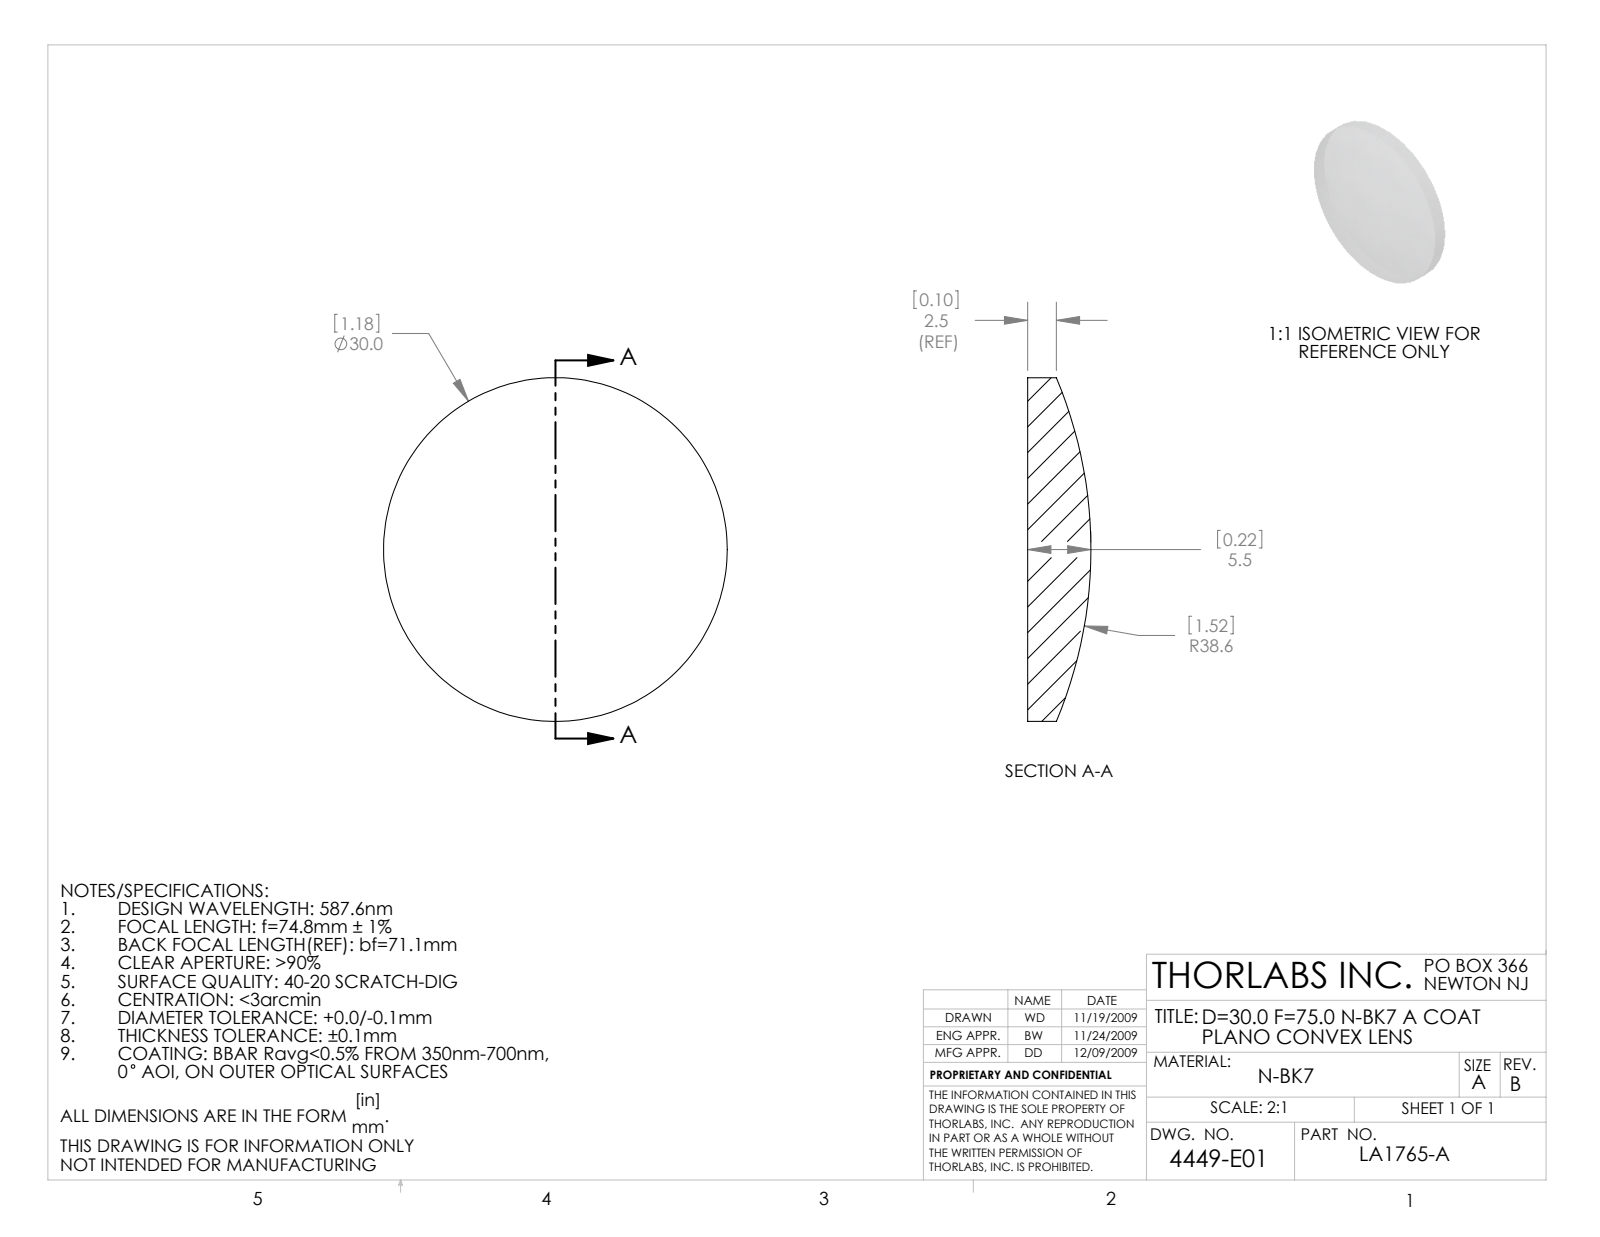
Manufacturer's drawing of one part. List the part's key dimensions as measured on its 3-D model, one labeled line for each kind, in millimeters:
Part name (STEP PRODUCT): 4449-E0W
STEP written by: SolidWorks 2009 (AUTOMOTIVE_DESIGN)
Units: millimetres
Bodies: 1 solid, 5 faces (1 planar, 2 cylindrical, 2 other)
Overall size (bounding box): 30 × 30 × 5.53
Volume: 2 852 mm³ · Surface area: 1 678 mm²
Round bosses / shafts (diameter × count): ⌀30 ×1
